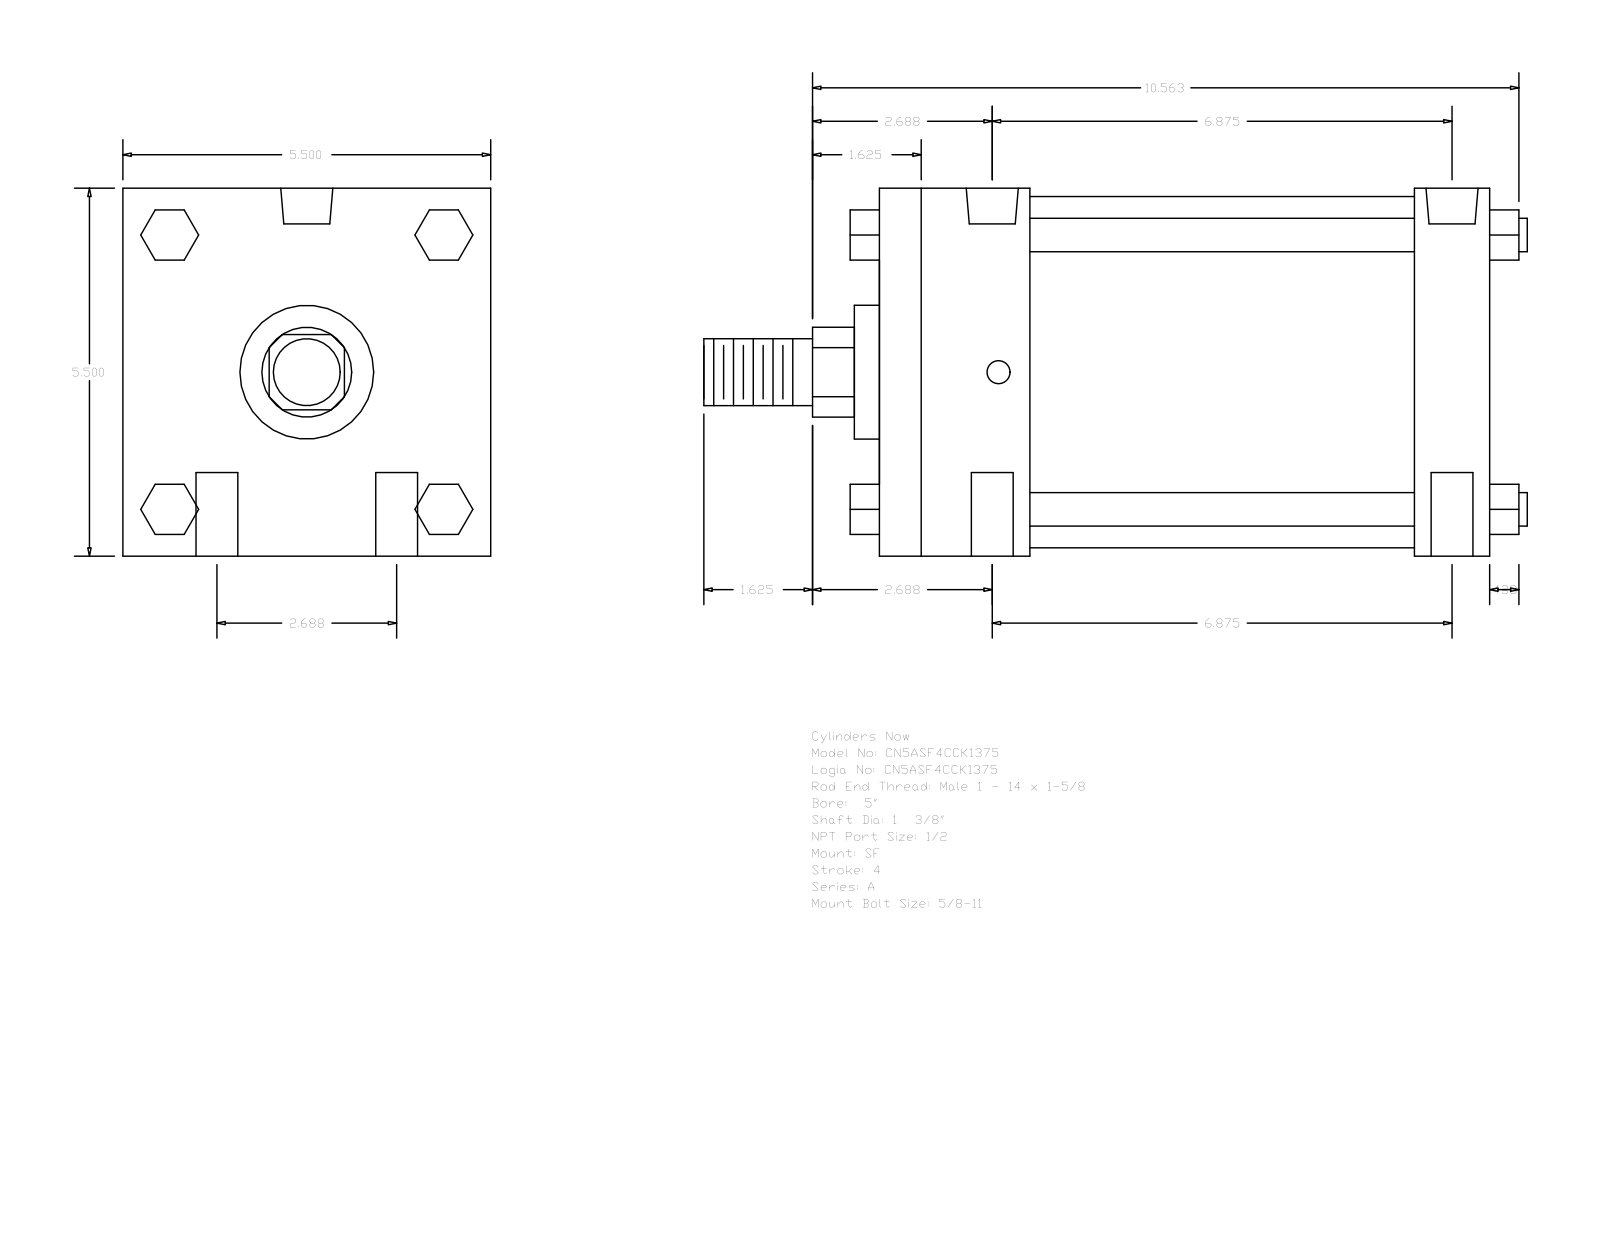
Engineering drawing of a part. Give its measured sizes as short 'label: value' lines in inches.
name: A_SF__0500_1.375
written by: GSSL Pune (CONFIG_CONTROL_DESIGN)
unit: in
bodies: 0 solids, 124 faces (94 planar, 30 cylindrical, 0 other)
size: 12.313 × 5.5 × 5.5
holes: 4× ⌀0.625, 2× ⌀0.344, 2× ⌀0.778
bosses: 4× ⌀0.5, 1× ⌀5.25, 1× ⌀2, 1× ⌀1.375, 1× ⌀1
rounds: 1× R0.672
face distances: 5.5, 9.125, 2.25, 1.125, 8, 5.75, 6.875, 0.75, 2.05, 3.55
hole spacings: 1.344, 7.005, 6.875, 2.687, 7.382, 6.687
